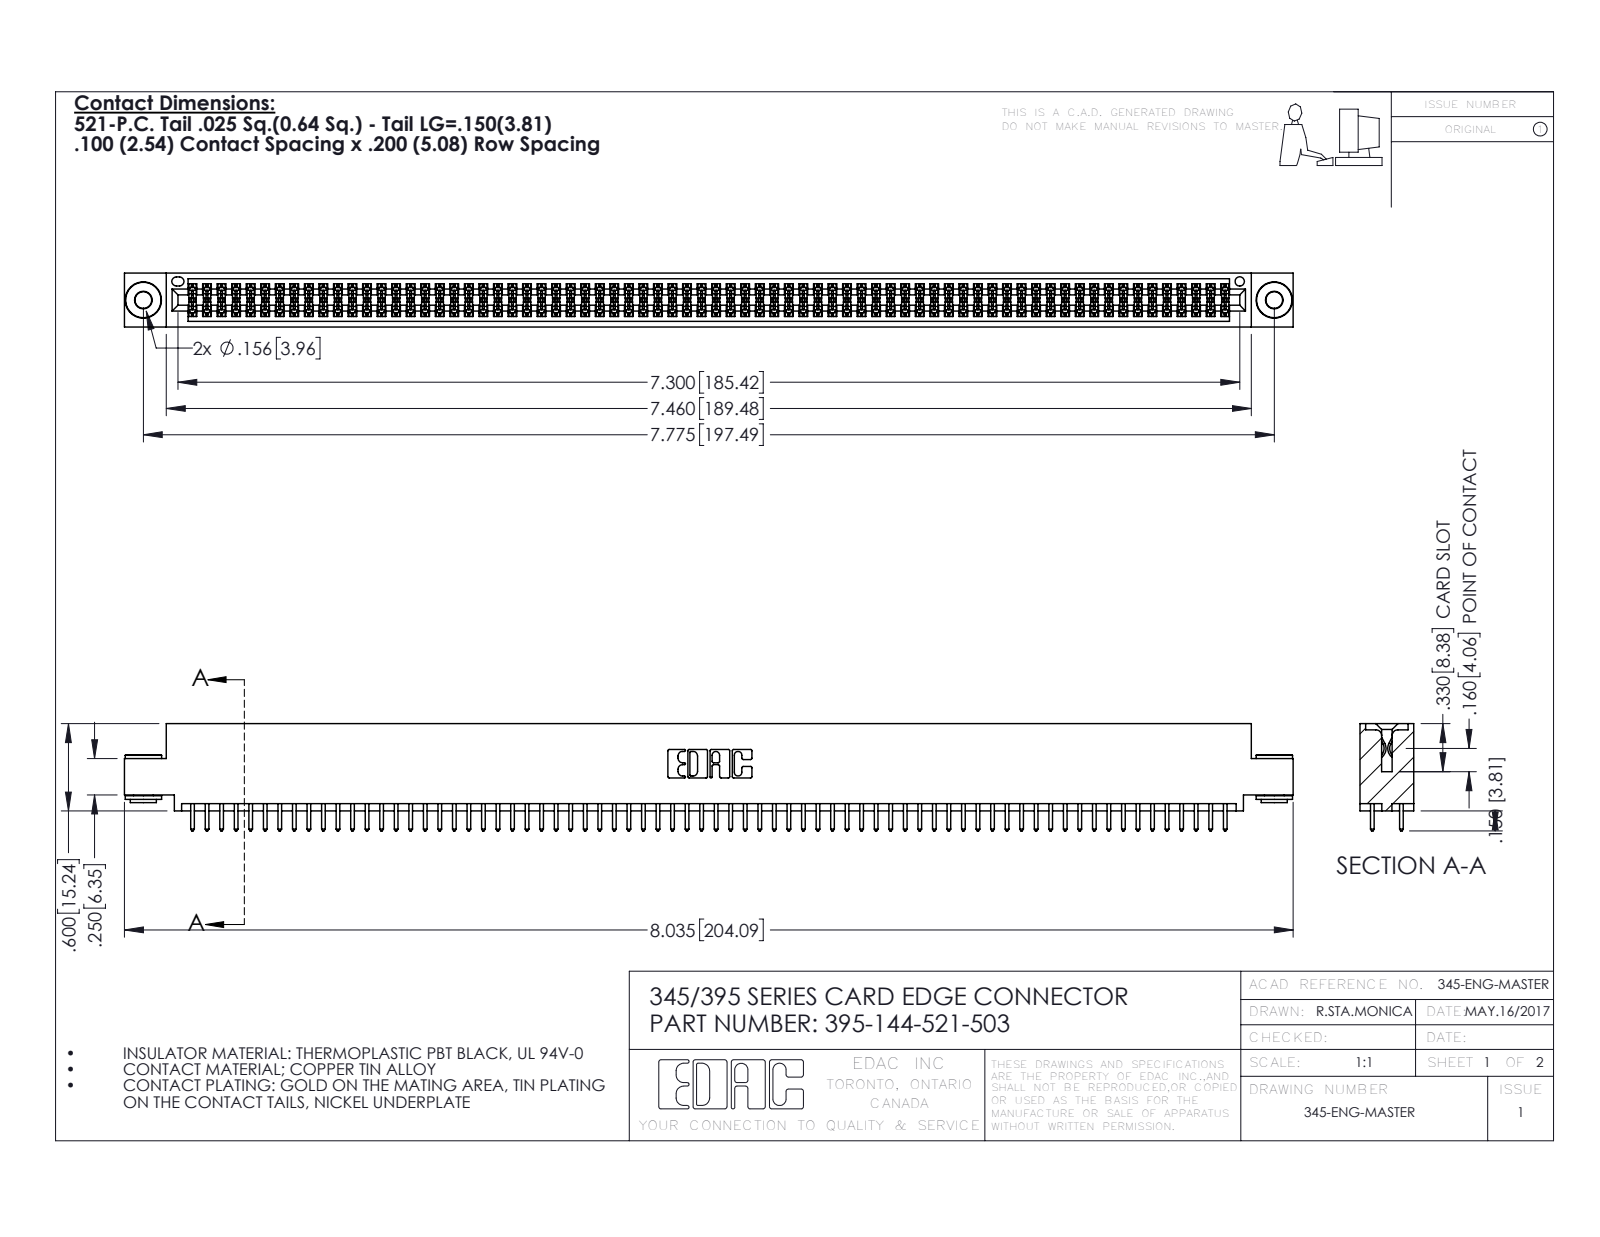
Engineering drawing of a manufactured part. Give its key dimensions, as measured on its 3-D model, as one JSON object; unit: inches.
{"part_name": "345 Part_0.110 Offset - 0.156 Dia-TH; 345-250-002_345-250-002-102; 345-292-001_345-293-121; 395-144-521-503", "step_written_by": "SolidWorks 2016 (CONFIG_CONTROL_DESIGN)", "units": "inches", "bodies": {"solids": 147, "faces": 7368, "planar": 4846, "cylindrical": 2514, "other": 8}, "overall_size": [8.035, 0.737, 0.37], "volume_in3": 1.22, "surface_area_in2": 46.57, "round_holes": [[0.116, 2], [0.156, 2], [0.064, 1]], "round_bosses_or_shafts": [[0.25, 2], [0.18, 2], [0.136, 2]], "partial_cylinders_radius": [[0.006, 216], [0.01, 144], [0.01, 22], [0.007, 6], [0.031, 6], [0.026, 3], [0.014, 2], [0.019, 2]], "face_to_face_distances": [0.072, 0.298, 0.2, 0.025, 0.098, 0.272, 0.37, 0.225, 0.175, 0.149], "hole_center_spacings": [0.27, 7.539, 7.775]}
